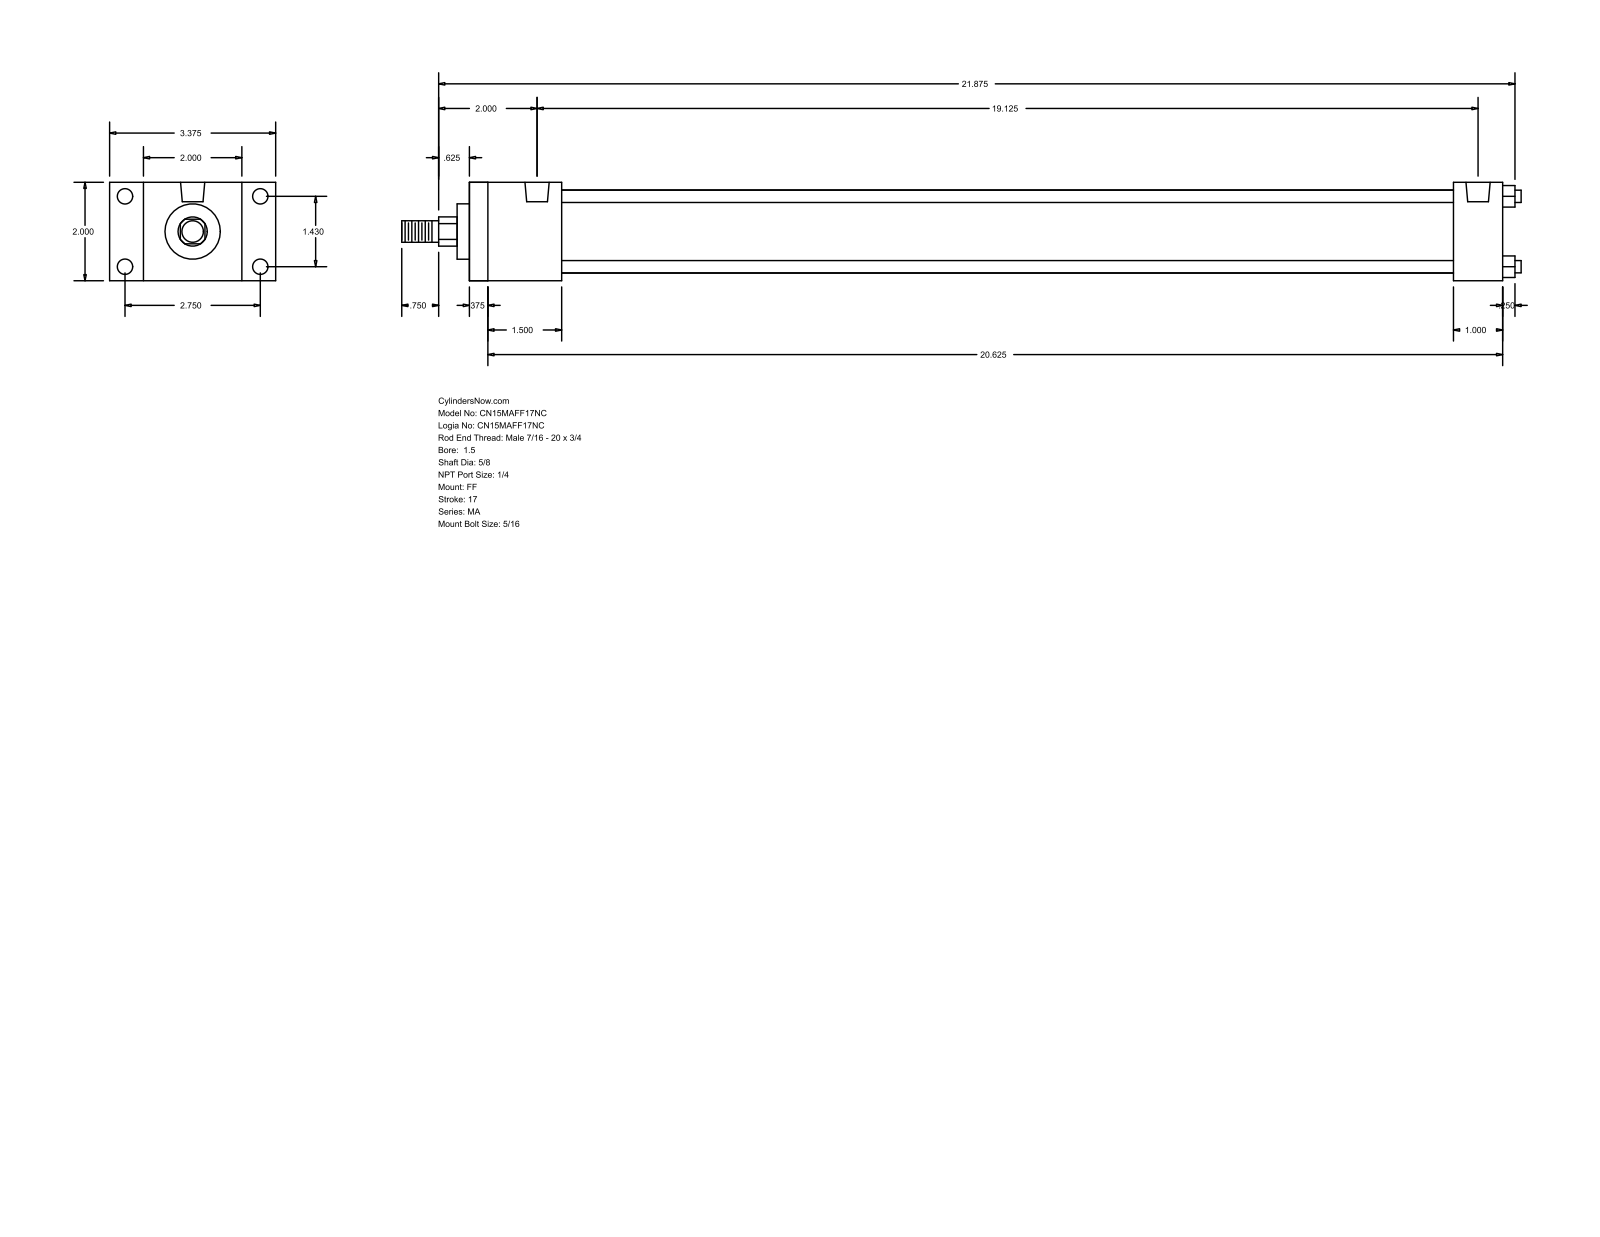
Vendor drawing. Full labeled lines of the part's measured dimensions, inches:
Part name (STEP PRODUCT): MA_FF__0150_0.625
STEP written by: GSSL Pune (CONFIG_CONTROL_DESIGN)
Units: inches
Bodies: 0 solids, 92 faces (64 planar, 28 cylindrical, 0 other)
Overall size (bounding box): 22.75 × 3.375 × 2
Round holes (diameter × count): ⌀0.313 ×8, ⌀0.492 ×2
Round bosses / shafts (diameter × count): ⌀0.25 ×4, ⌀1.69 ×1, ⌀1.125 ×1, ⌀0.625 ×1, ⌀0.437 ×1
Partial cylindrical surfaces — rounded edges, fillets, slot ends (radius × count): R0.297 ×1
Main face-to-face distances: 2, 21, 0.375, 20.625, 1.875, 20, 1.5, 19.625, 18.125, 19.125
Hole centre spacings: 1.43, 2.75, 3.099, 19.125
